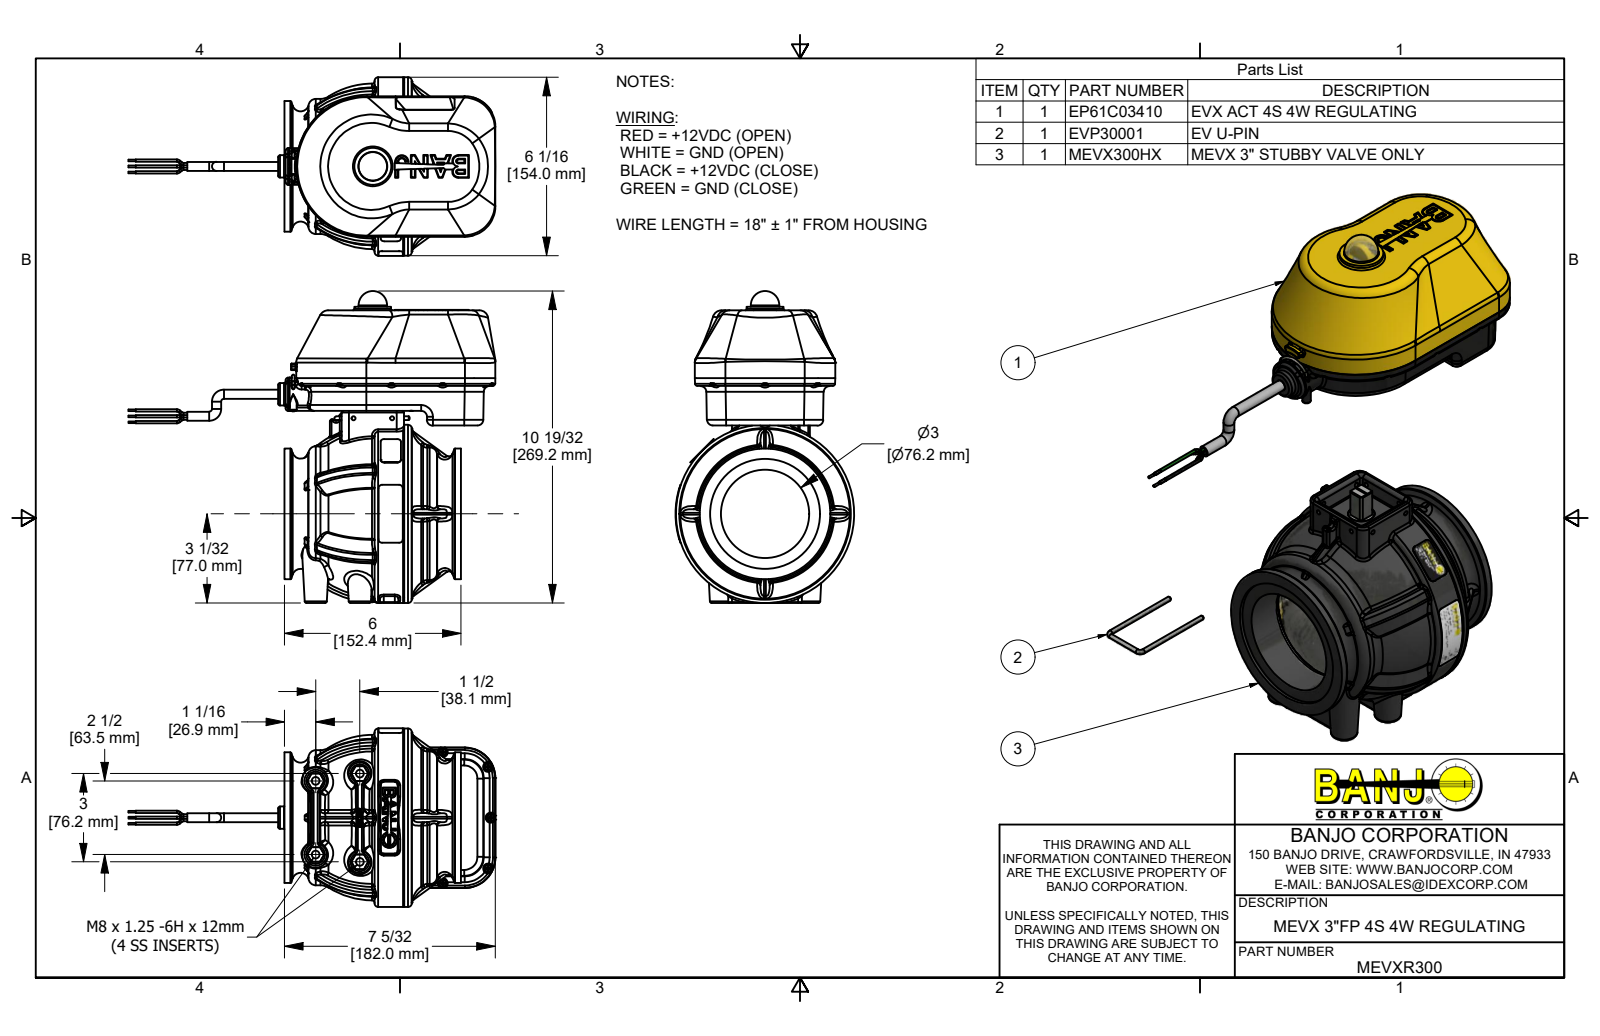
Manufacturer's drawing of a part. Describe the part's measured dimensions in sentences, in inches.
The part is named "MEVXR300; EP61C03410; 91400A119; 91841A005 (+8 more)". Its 3-D file was written by "Autodesk Inventor 2019 (AUTOMOTIVE_DESIGN)". It is 80 solids with 9453 faces: 3630 planar, 3076 cylindrical and 2747 other. Overall it measures 12.476 by 10.6 by 6.072 inches. Its volume is 89.64 cubic inches and its surface area 892.3 square inches. Round holes: 11 of diameter 0.095, 11 of diameter 0.15, 11 of diameter 0.34, 6 of diameter 0.135, 4 of diameter 0.104, 4 of diameter 0.136, 4 of diameter 0.176, 4 of diameter 0.262, 4 of diameter 0.266, 4 of diameter 0.433, 2 of diameter 0.089, 2 of diameter 0.105. Round bosses or shafts: 20 of diameter 0.08, 19 of diameter 0.25, 11 of diameter 0.14, 11 of diameter 0.108, 11 of diameter 0.085, 8 of diameter 0.058, 4 of diameter 0.437, 4 of diameter 0.375. Partial cylindrical surfaces (rounded edges, fillets, slot ends): 138 of radius 0.405, 114 of radius 0.387, 112 of radius 0.309, 108 of radius 0.253, 106 of radius 0.609, 68 of radius 0.01, 46 of radius 0.04, 43 of radius 0.05. The main face-to-face distances are 0.083, 0.5, 0.085, 0.181, 0.096, 2.175, 2.356, 2.271, 0.125, 0.1. The hole center spacings are 3.316, 1.115, 1.313, 2.259, 0.55, 0.611, 0.646, 0.663.
